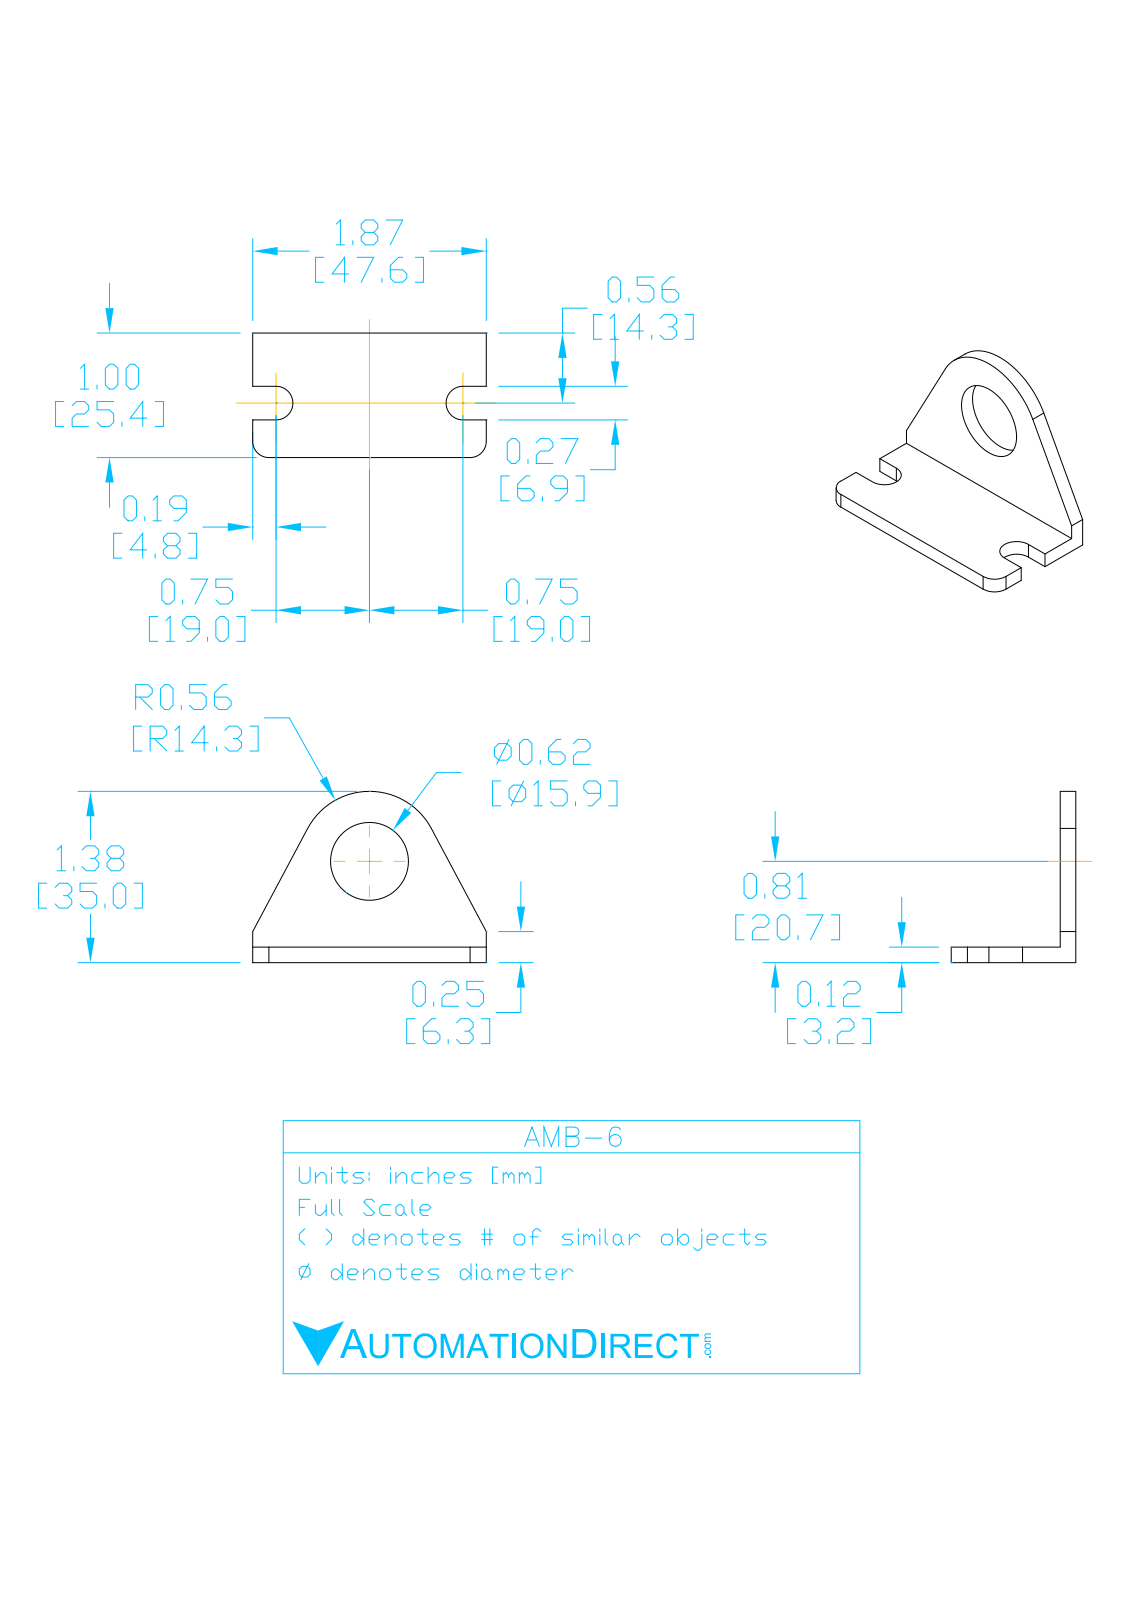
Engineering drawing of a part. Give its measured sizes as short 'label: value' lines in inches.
name: AMB-6
written by: SolidWorks 2017 (AUTOMOTIVE_DESIGN)
unit: in
bodies: 1 solid, 28 faces (19 planar, 9 cylindrical, 0 other)
size: 1.874 × 1.378 × 1
volume: 0.369 in³; area: 7.153 in²
holes: 1× ⌀0.626
rounds: 2× R0.135, 2× R0.187, 1× R0.03, 1× R0.155, 1× R0.56
face distances: 0.125, 0.125, 0.875, 1, 1.874, 0.302, 0.573, 0.698, 0.572, 0.27
